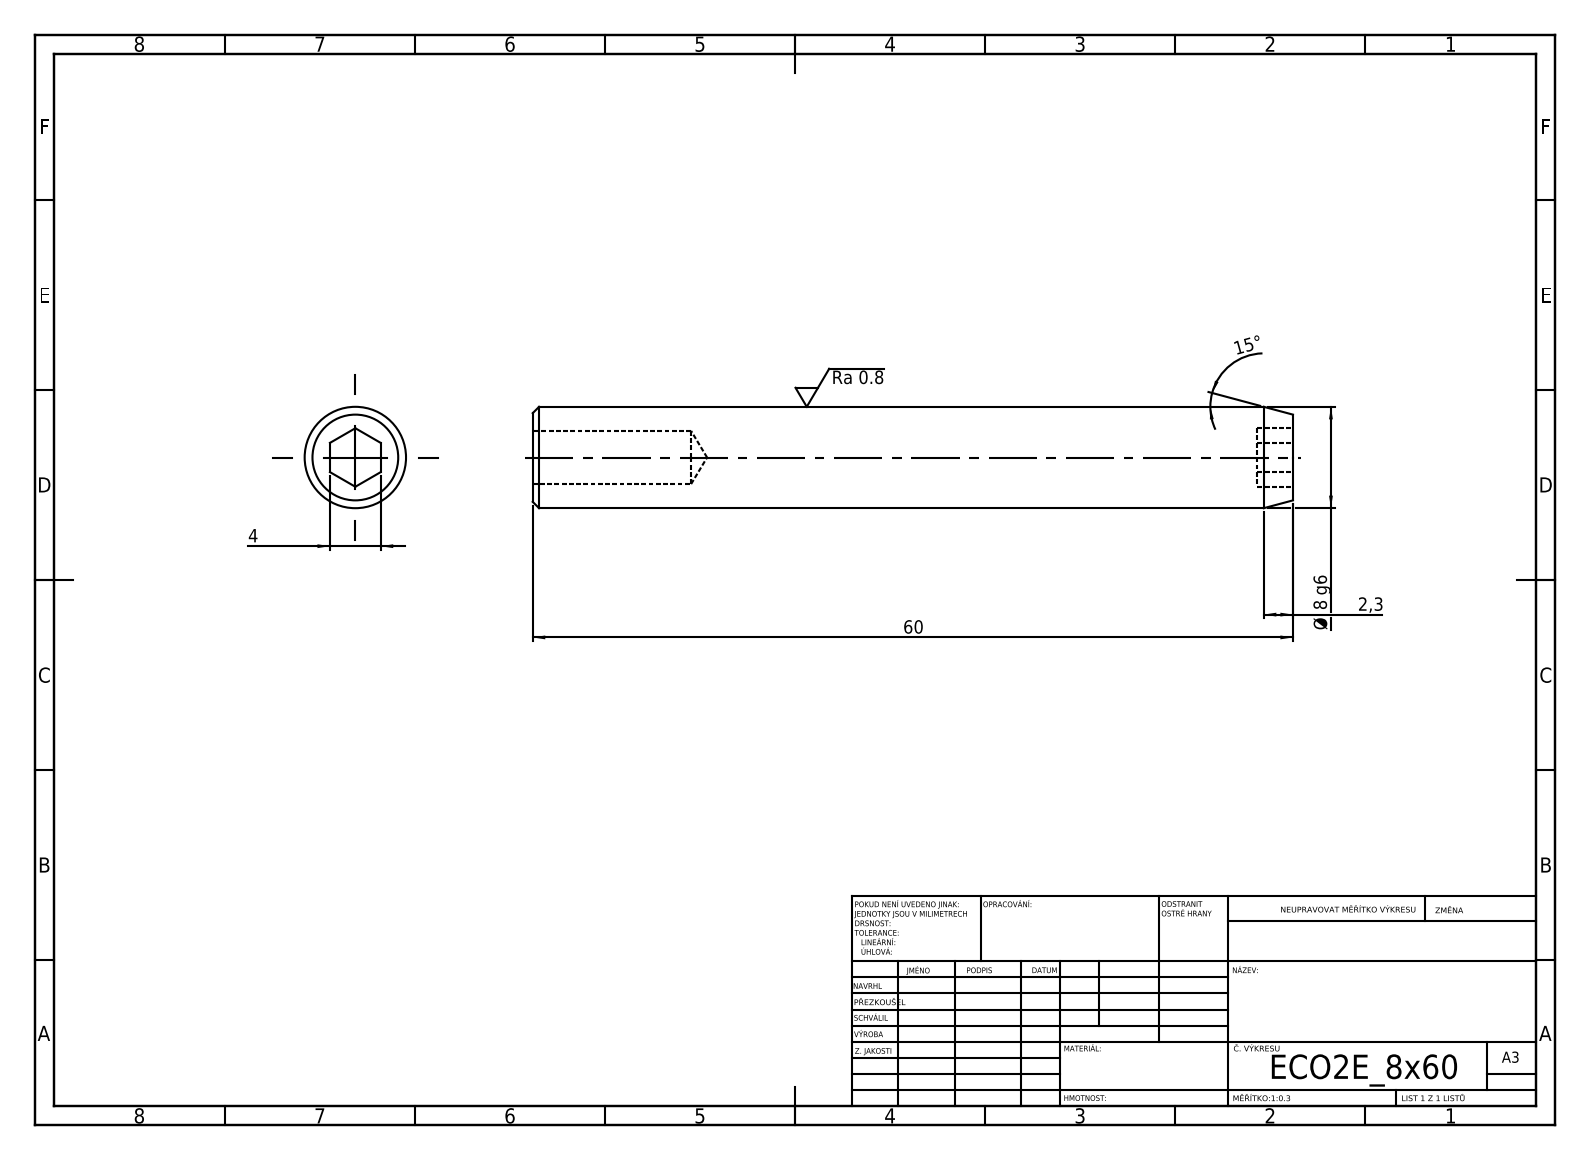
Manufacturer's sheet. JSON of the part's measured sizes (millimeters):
{"step_written_by": "SolidWorks 2019 (CONFIG_CONTROL_DESIGN)", "units": "millimeters", "bodies": {"solids": 1, "faces": 19, "planar": 9, "cylindrical": 4, "other": 6}, "overall_size": [60, 8, 8], "volume_mm3": 2778, "surface_area_mm2": 1790, "round_holes": [[4.2, 1]], "round_bosses_or_shafts": [[8, 1]], "face_to_face_distances": [60, 4, 2.8, 57.2]}
